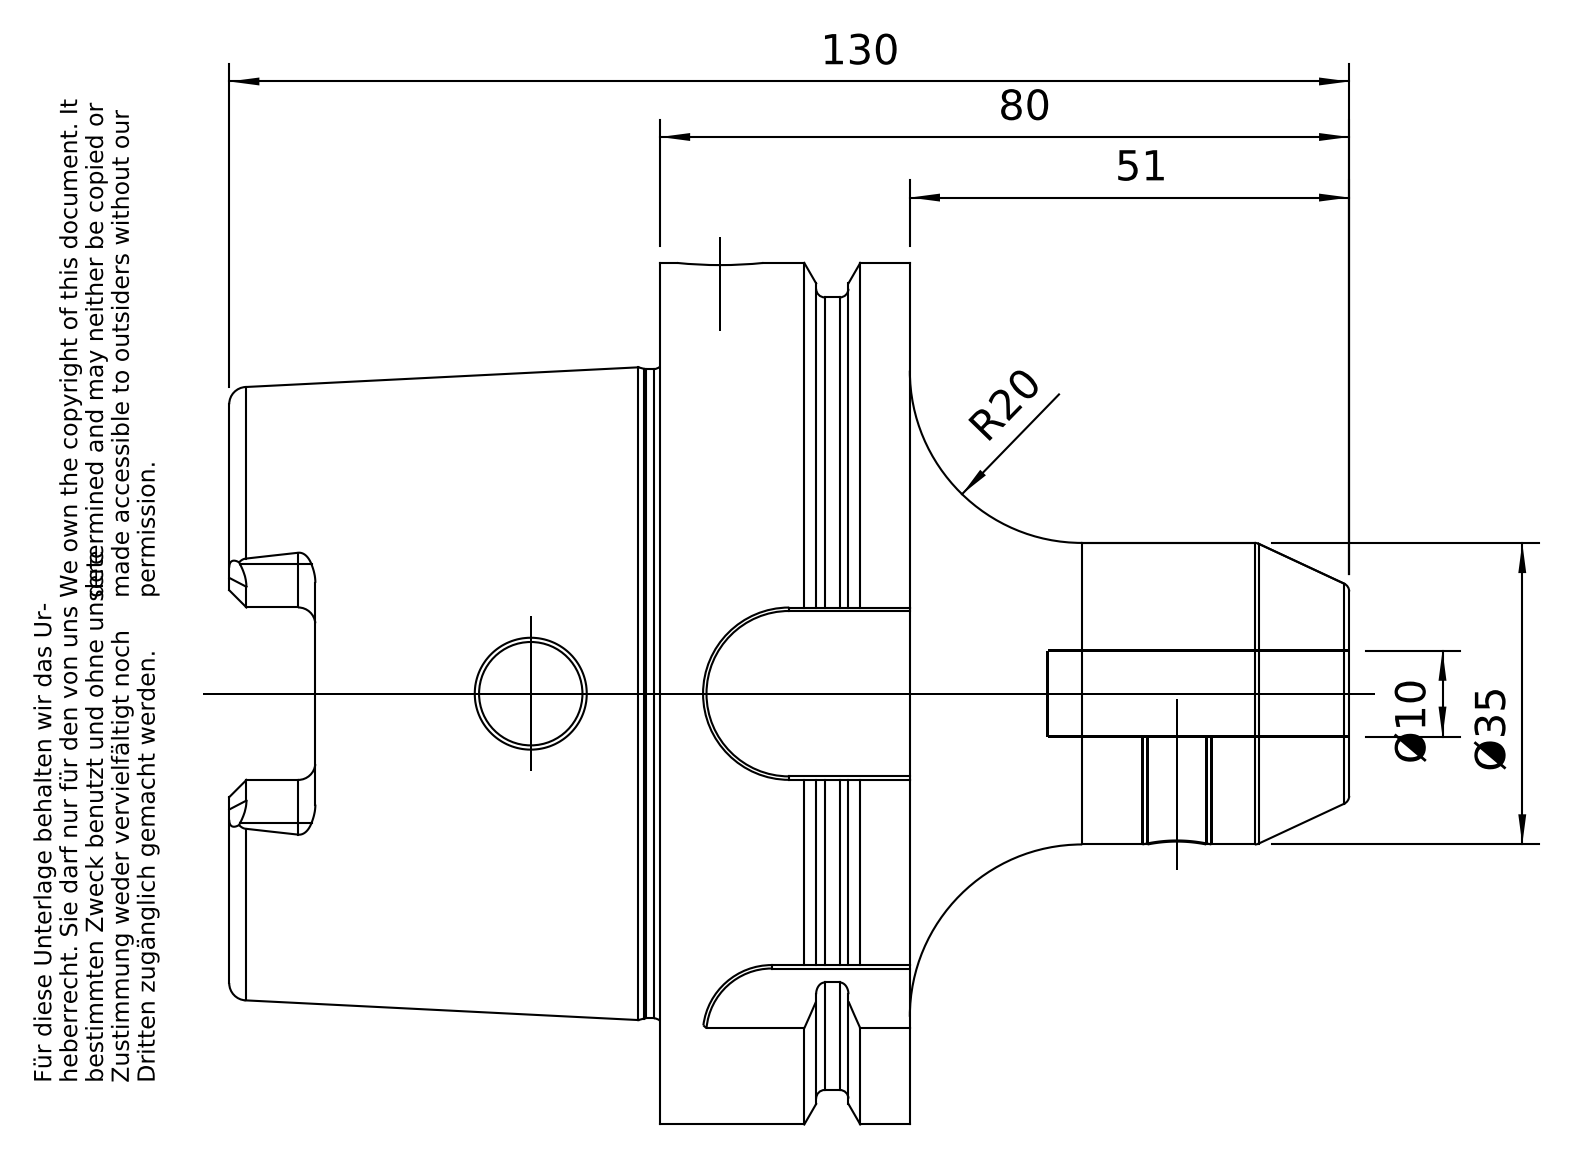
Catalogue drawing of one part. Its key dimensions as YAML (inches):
part_name: "A100-000-10"
step_written_by: "PRO/ENGINEER BY PARAMETRIC TECHNOLOGY CORPORATION, 2010430 (CONFIG_CONTROL_DESIGN)"
units: inches
bodies: {solids: 1, faces: 182, planar: 52, cylindrical: 55, other: 75}
overall_size: [5.118, 3.937, 3.937]
volume: 18.87
surface_area: 87.05
round_holes:
  - {diameter: 0.394, count: 2}
  - {diameter: 0.268, count: 1}
  - {diameter: 0.315, count: 1}
  - {diameter: 0.472, count: 1}
  - {diameter: 0.886, count: 1}
  - {diameter: 0.945, count: 1}
  - {diameter: 0.957, count: 1}
  - {diameter: 0.965, count: 1}
  - {diameter: 2.087, count: 1}
  - {diameter: 2.48, count: 1}
round_bosses_or_shafts:
  - {diameter: 3.937, count: 1}
  - {diameter: 3.622, count: 1}
  - {diameter: 2.967, count: 1}
  - {diameter: 1.378, count: 1}
partial_cylinders:
  - {radius: 0.079, count: 6}
  - {radius: 0.197, count: 4}
  - {radius: 0.315, count: 1}
  - {radius: 0.394, count: 1}
  - {radius: 0.433, count: 1}
face_to_face_distances: [1.142, 0.492, 0.65, 1.969, 2.461, 3.11, 0.63, 3.15, 3.465, 3.091]
hole_center_spacings: [2.087]
